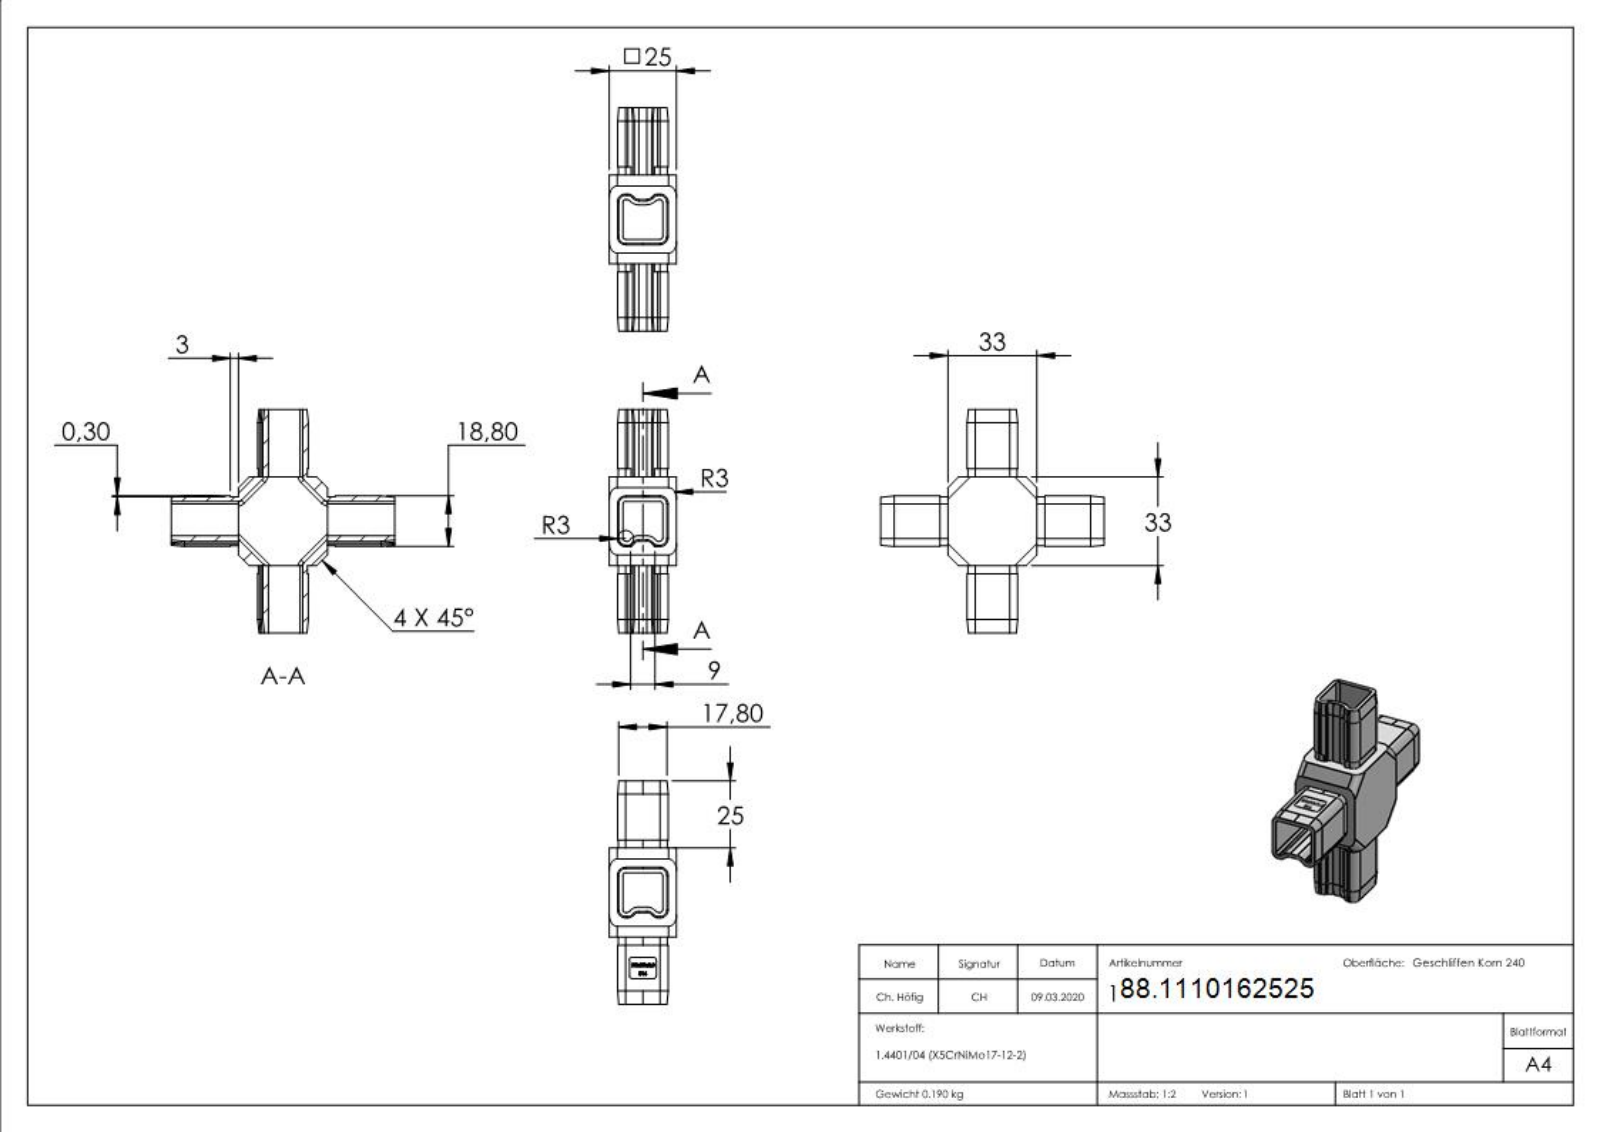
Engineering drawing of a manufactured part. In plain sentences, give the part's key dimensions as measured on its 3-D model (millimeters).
The part is named "10162525". Its 3-D file was written by "SolidWorks 2015 (CONFIG_CONTROL_DESIGN)". It is 1 solid with 731 faces: 384 planar, 124 cylindrical and 223 other. Overall it measures 83 by 83 by 25 millimeters. Its volume is 25 102 cubic millimeters and its surface area 21 221 square millimeters. Partial cylindrical surfaces (rounded edges, fillets, slot ends): 30 of radius 1.5, 16 of radius 3, 12 of radius 1, 8 of radius 2.7, 4 of radius 2.46, 4 of radius 2.46, 2 of radius 0.46, 2 of radius 4.46. The main face-to-face distances are 2, 16.8, 18.8, 4.1, 22.9, 2.1, 20.9, 25, 20.8, 8.1.
